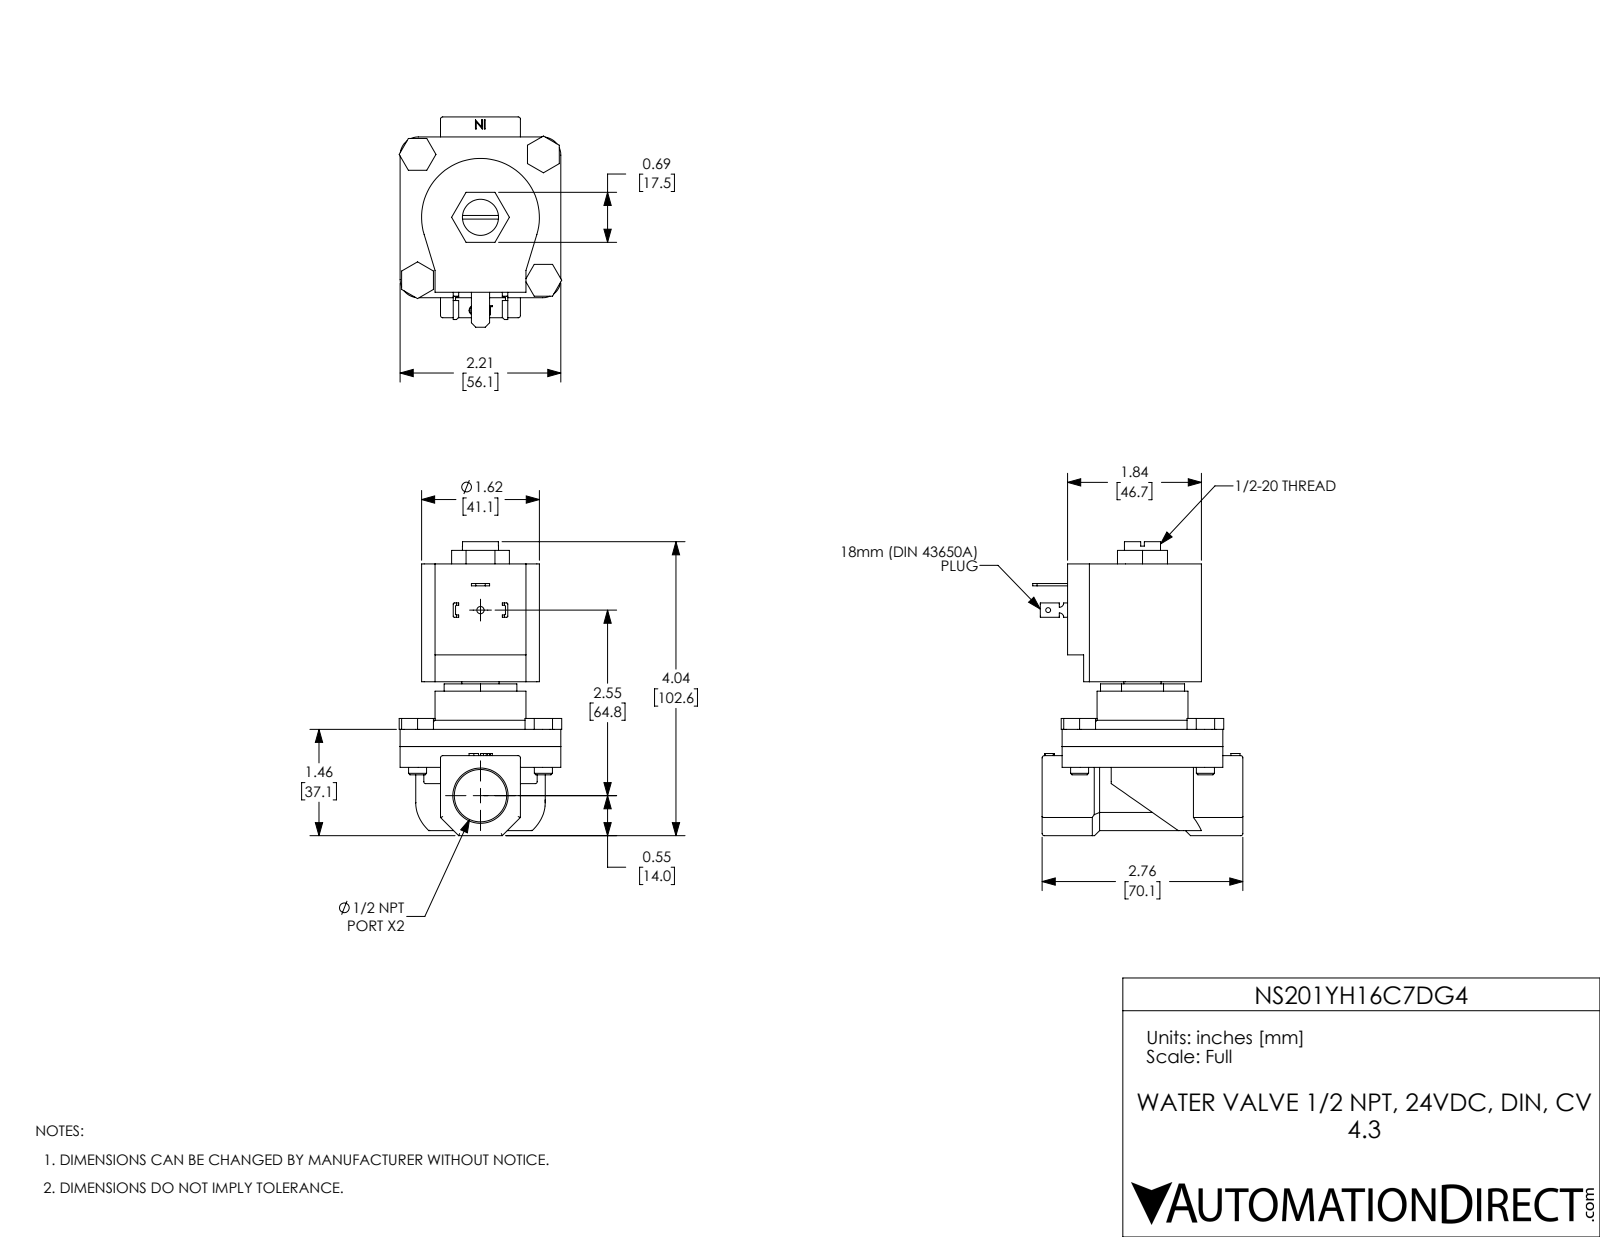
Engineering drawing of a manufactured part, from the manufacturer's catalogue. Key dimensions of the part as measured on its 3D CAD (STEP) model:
Part name (STEP PRODUCT): NS201YH16C7DG4
STEP written by: SolidWorks 2024 (CONFIG_CONTROL_DESIGN)
Units: inches
Bodies: 11 solids, 330 faces (196 planar, 99 cylindrical, 35 other)
Overall size (bounding box): 4.04 × 2.89 × 2.235
Volume: 9.842 in³ · Surface area: 63.61 in²
Round holes (diameter × count): ⌀0.25 ×4, ⌀0.067 ×1, ⌀0.1 ×1, ⌀0.496 ×1, ⌀0.512 ×1, ⌀0.72 ×1, ⌀1.155 ×1
Round bosses / shafts (diameter × count): ⌀0.248 ×4, ⌀1.25 ×1
Partial cylindrical surfaces — rounded edges, fillets, slot ends (radius × count): R0.03 ×15, R0.015 ×8, R0.25 ×4, R0.06 ×2, R0.81 ×1, R0.89 ×1
Main face-to-face distances: 0.237, 0.237, 2.51, 2.51, 2.273, 0.556, 1.654, 0.286, 0.286, 0.523
Hole centre spacings: 1.223, 1.73, 2.446, 2.55
